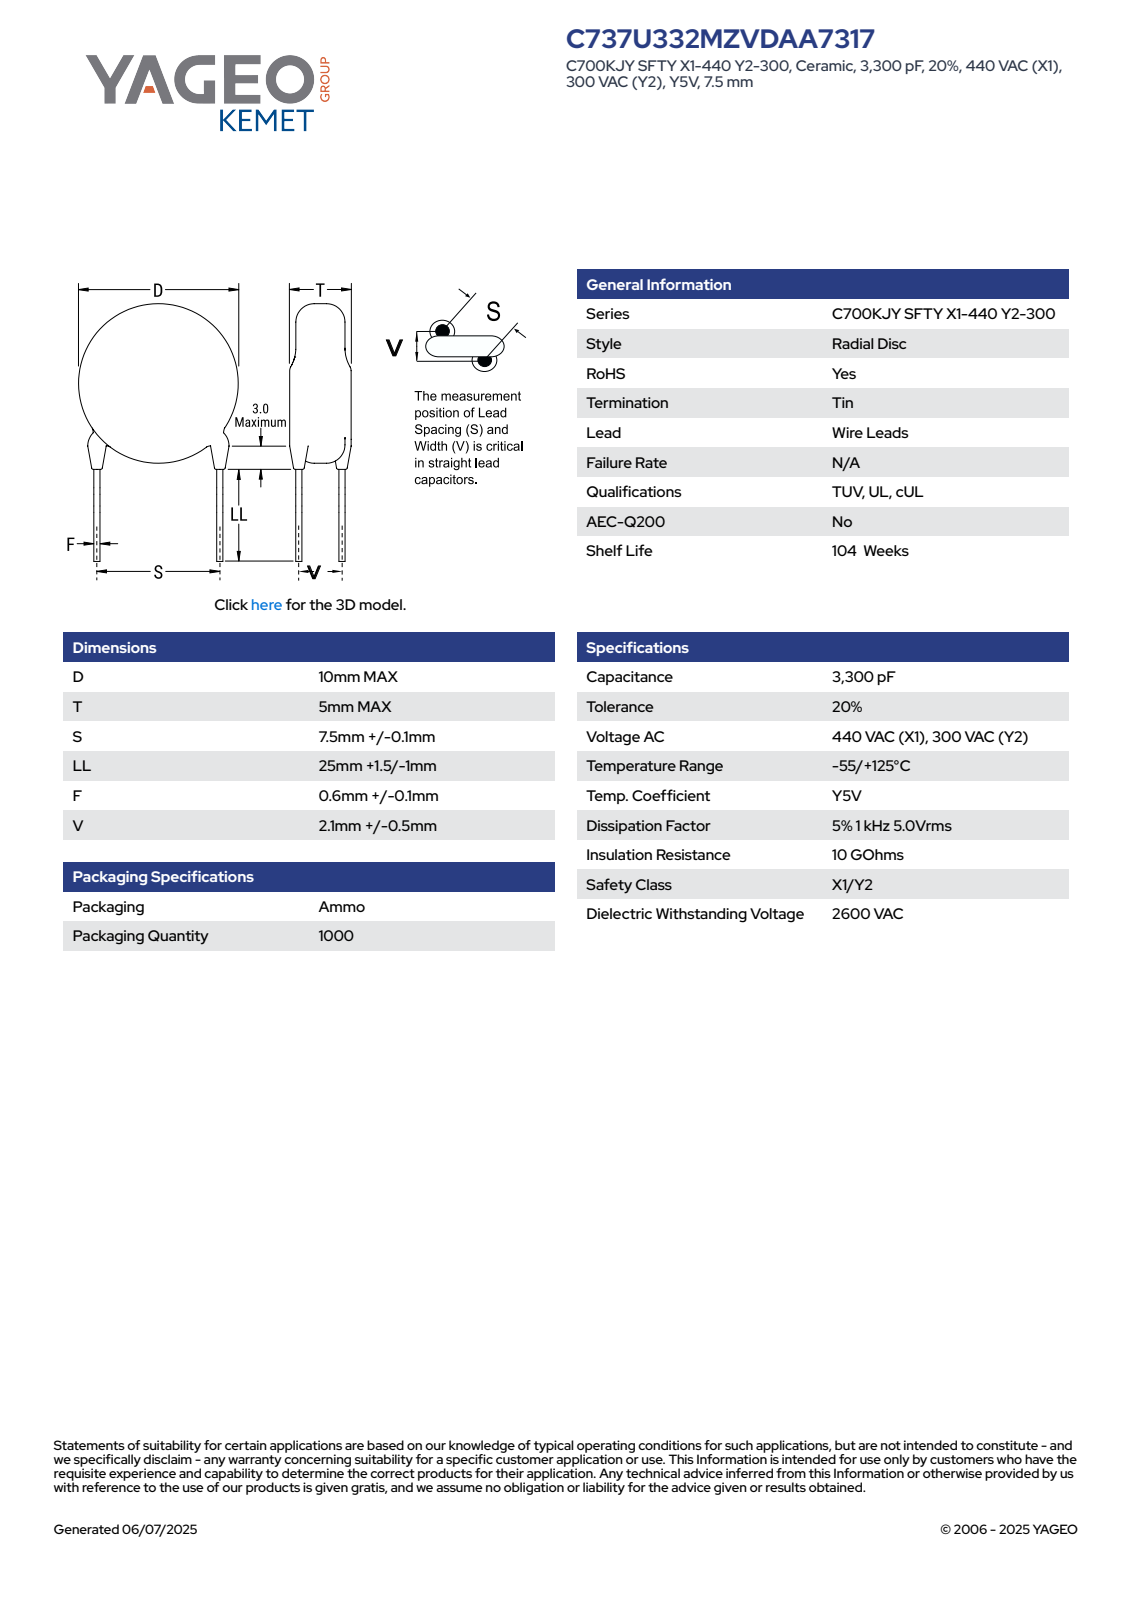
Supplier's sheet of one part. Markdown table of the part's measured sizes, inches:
| quantity | value |
| --- | --- |
| part name | CCD_KST_10X5_D10T5S7.6LL26.5F0.7V2.1 |
| STEP written by | SolidWorks 2021 (AUTOMOTIVE_DESIGN) |
| units | inches |
| bodies | 4 solids, 80 faces (63 planar, 13 cylindrical, 4 other) |
| overall size | 1.481 × 0.394 × 0.197 |
| volume | 0.025 in³ |
| surface area | 0.67 in² |
| round bosses / shafts (diameter × count) | 0.047 × 2, 0.028 × 2, 0.394 × 1 |
| partial cylindrical surfaces (radius × count) | 0.024 × 2 |
| main face-to-face distances | 0.197, 1.043, 1.312, 0.269, 1.267, 0.223, 0.046, 0.013, 0.037, 0.02 |
